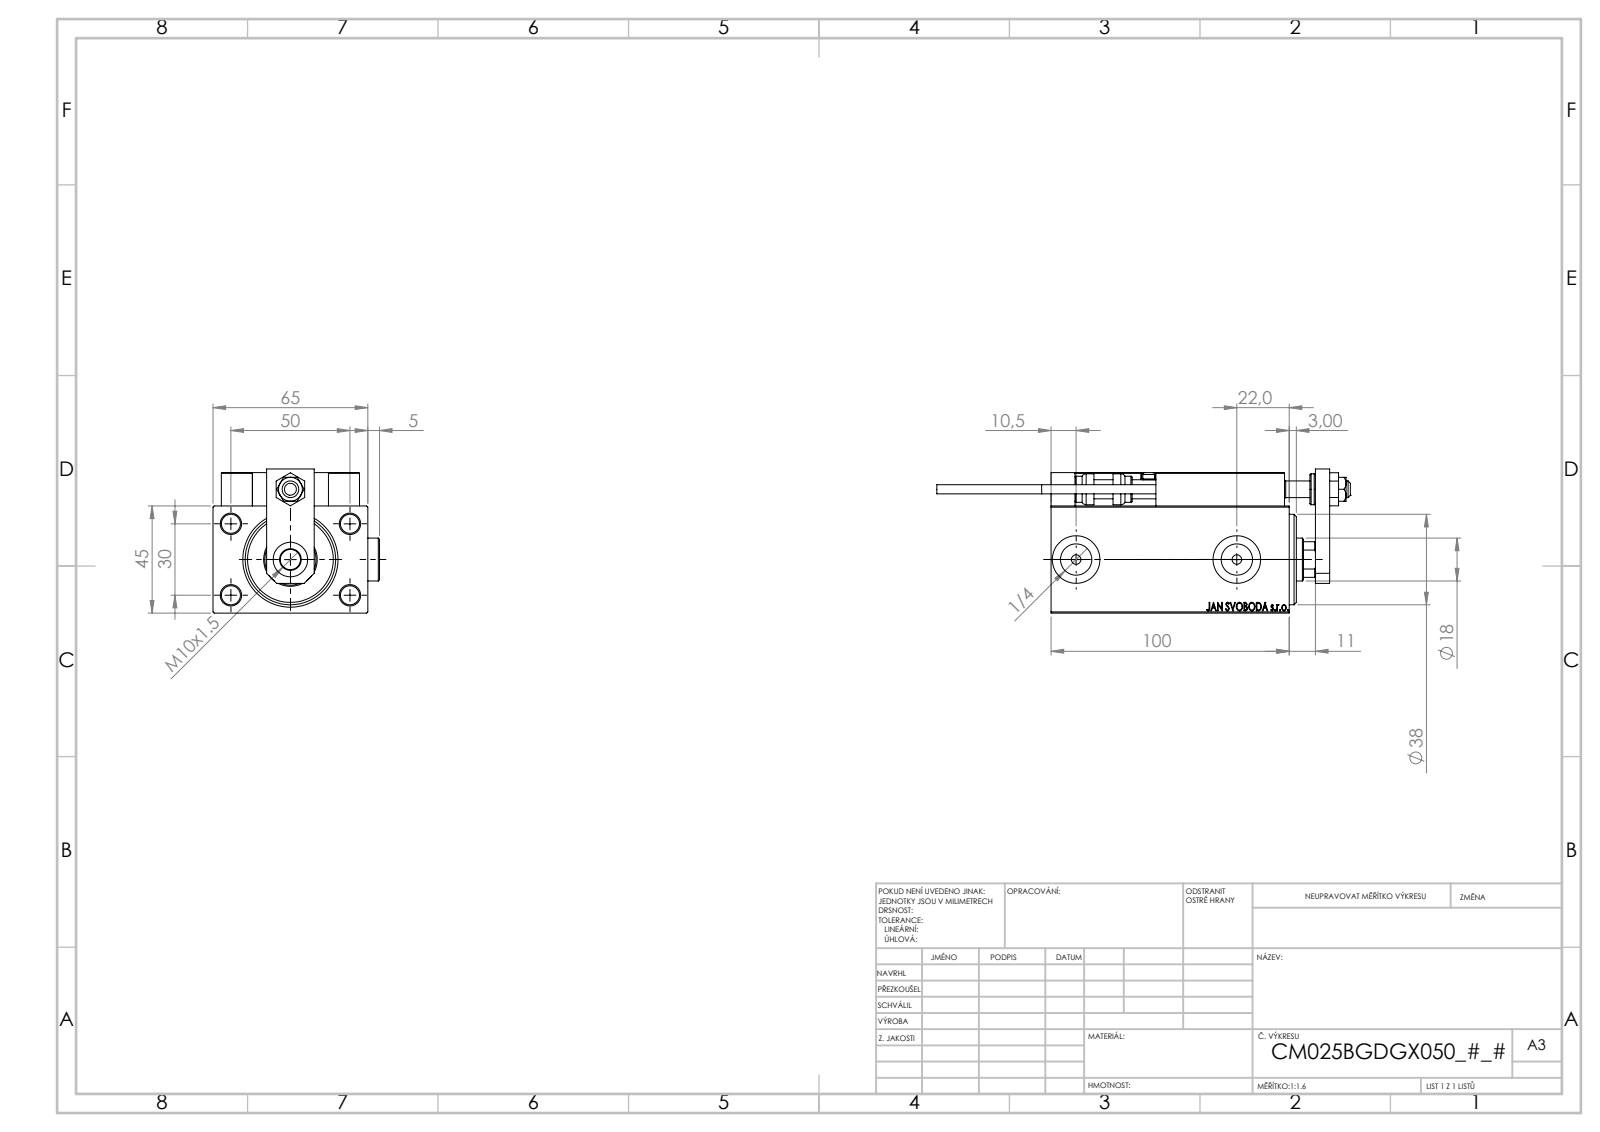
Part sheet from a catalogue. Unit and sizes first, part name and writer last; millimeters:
Units: millimetres
Overall size (bounding box): 173.7 × 69.9 × 60.5
Round holes (diameter × count): ⌀8 ×9, ⌀4 ×6, ⌀3.2 ×4, ⌀5 ×2, ⌀13.16 ×2, ⌀20 ×2, ⌀7 ×1, ⌀8.5 ×1, ⌀14.5 ×1, ⌀18 ×1, ⌀21.5 ×1, ⌀22.5 ×1
Round bosses / shafts (diameter × count): ⌀18 ×2, ⌀5 ×2, ⌀3.8 ×2, ⌀13 ×1, ⌀11 ×1
Partial cylindrical surfaces — rounded edges, fillets, slot ends (radius × count): R0.3 ×30, R3 ×2, R8.5 ×1
Main face-to-face distances: 45, 65, 14, 6, 59, 5, 13, 3.5, 111, 19
Hole centre spacings: 29.15, 11.37, 20, 28.9, 29.59, 29.69, 30, 36.06
Volume: 319 649 mm³ · Surface area: 78 592 mm²
Bodies: 26 solids, 1372 faces (595 planar, 200 cylindrical, 577 other)
Part name (STEP PRODUCT): Zatka_OIL_PORT; ALLEN BOLT D8; V450CM_B_Body; V450CM_B_VCP (+7 more)
STEP written by: SolidWorks 2019 (CONFIG_CONTROL_DESIGN)
